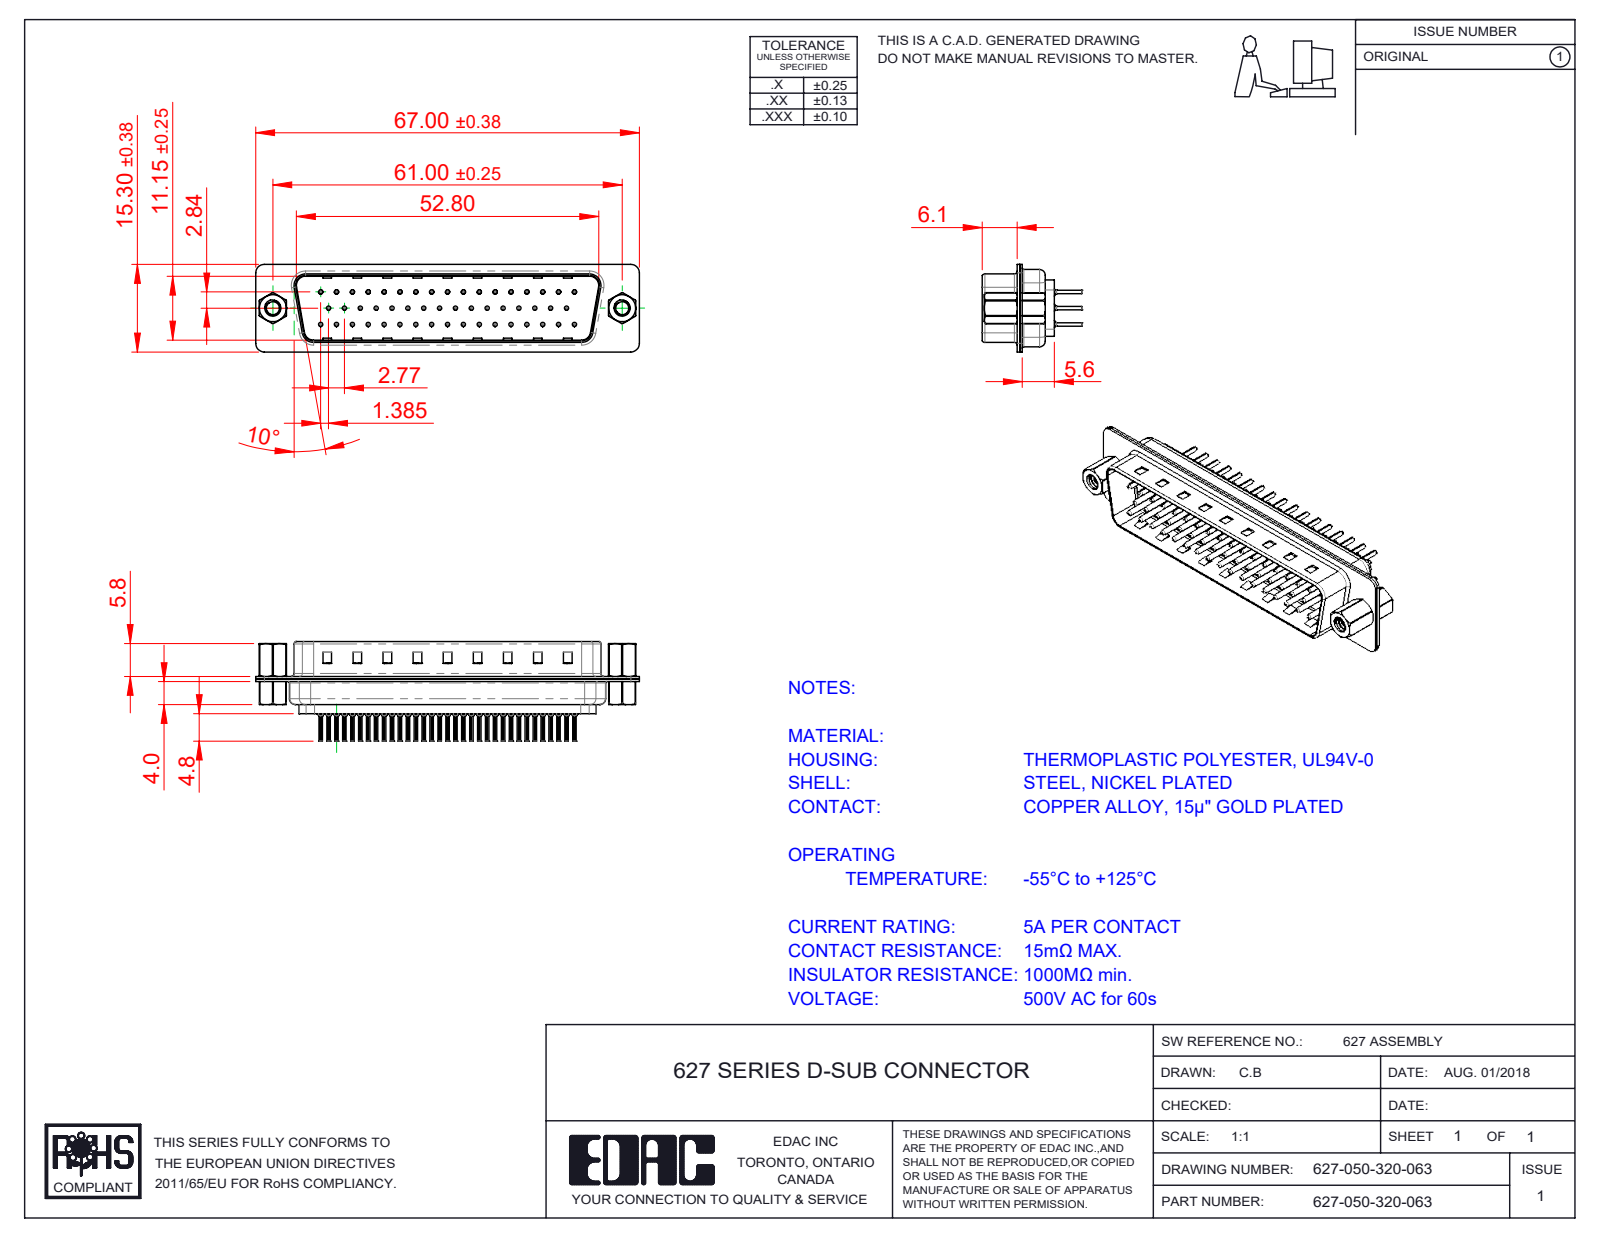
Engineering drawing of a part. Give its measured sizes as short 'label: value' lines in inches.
name: 627 Contact Row 3_20L; 627 Contact Row 2_20L; 627 Shell Front_50 Contacts; 627 4-40 Threaded Rivet (+5 more)
written by: SolidWorks 2020 (CONFIG_CONTROL_DESIGN)
unit: in
bodies: 57 solids, 5434 faces (1425 planar, 2061 cylindrical, 1948 other)
size: 2.638 × 0.681 × 0.602
volume: 0.283 in³; area: 20.24 in²
holes: 50× ⌀0.008, 50× ⌀0.014, 50× ⌀0.043, 50× ⌀0.063, 2× ⌀0.089, 2× ⌀0.09, 2× ⌀0.157, 2× ⌀0.189
bosses: 50× ⌀0.079, 50× ⌀0.059, 50× ⌀0.03, 50× ⌀0.024, 2× ⌀0.197, 2× ⌀0.193, 2× ⌀0.11
rounds: 100× R0.004, 16× R0.059, 12× R0.079, 8× R0.02, 8× R0.063, 4× R0.01, 4× R0.024, 4× R0.026
face distances: 0.016, 0.018, 0.455, 0.035, 0.238, 0.256, 0.031, 0.485, 0.077, 0.03
hole spacings: 0.124, 0.109, 0.218, 0.327, 0.436, 0.545, 0.654, 0.198
